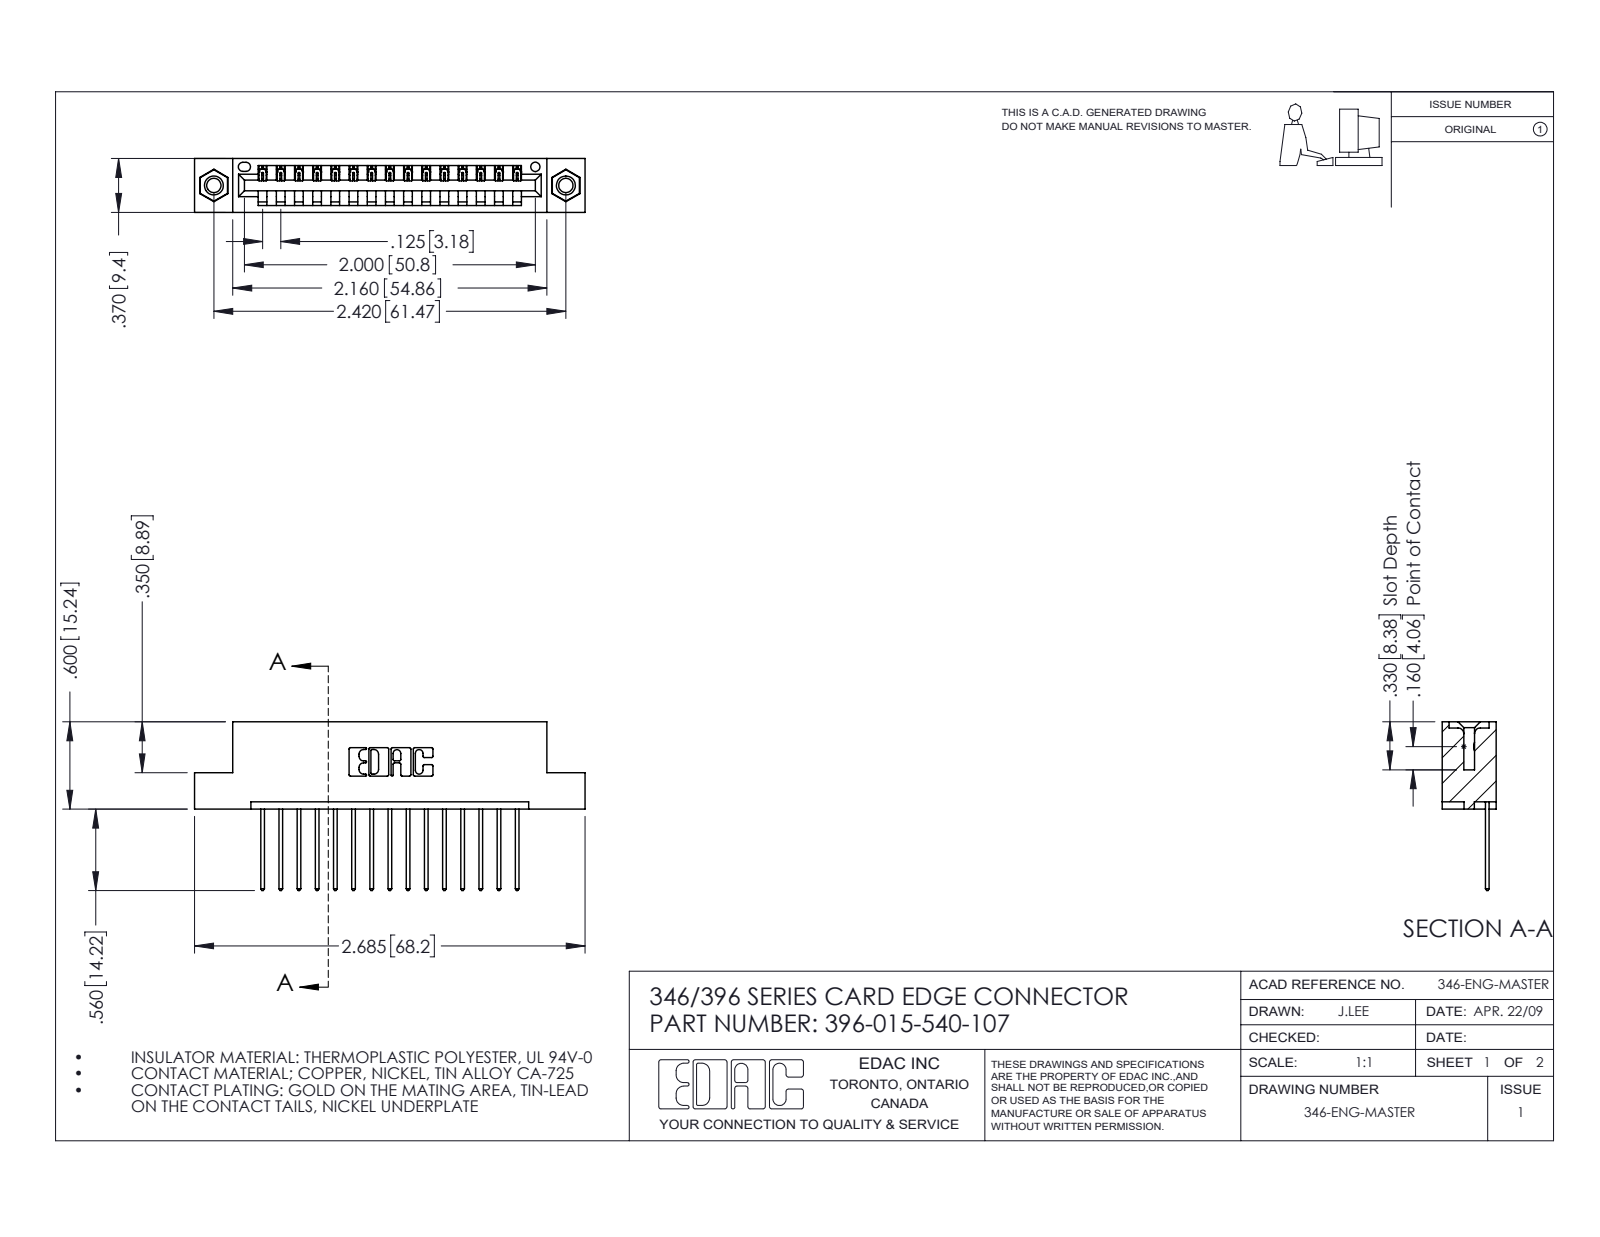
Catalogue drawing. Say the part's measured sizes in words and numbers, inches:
The part is named "345-250-001_345-250-005-103; 345-292-001_345-293-140; 346 Part_Flush Mounting Lugs - 0.156 Dia-TI; 396-015-540-107". Its 3-D file was written by "SolidWorks 2016 (CONFIG_CONTROL_DESIGN)". It is 18 solids with 1052 faces: 708 planar, 328 cylindrical and 16 other. Overall it measures 2.685 by 1.16 by 0.37 inches. Its volume is 0.387 cubic inches and its surface area 12.13 square inches. Round holes: 2 of diameter 0.098, 2 of diameter 0.125, 2 of diameter 0.156, 1 of diameter 0.064. Round bosses or shafts: 2 of diameter 0.155. Partial cylindrical surfaces (rounded edges, fillets, slot ends): 30 of radius 0.006, 30 of radius 0.01, 22 of radius 0.01, 6 of radius 0.007, 6 of radius 0.031, 3 of radius 0.026, 2 of radius 0.031, 2 of radius 0.04. The main face-to-face distances are 0.048, 0.322, 0.25, 0.37, 0.072, 0.298, 0.025, 0.148, 0.222, 0.1. The hole center spacings are 0.246, 2.213, 2.42.
